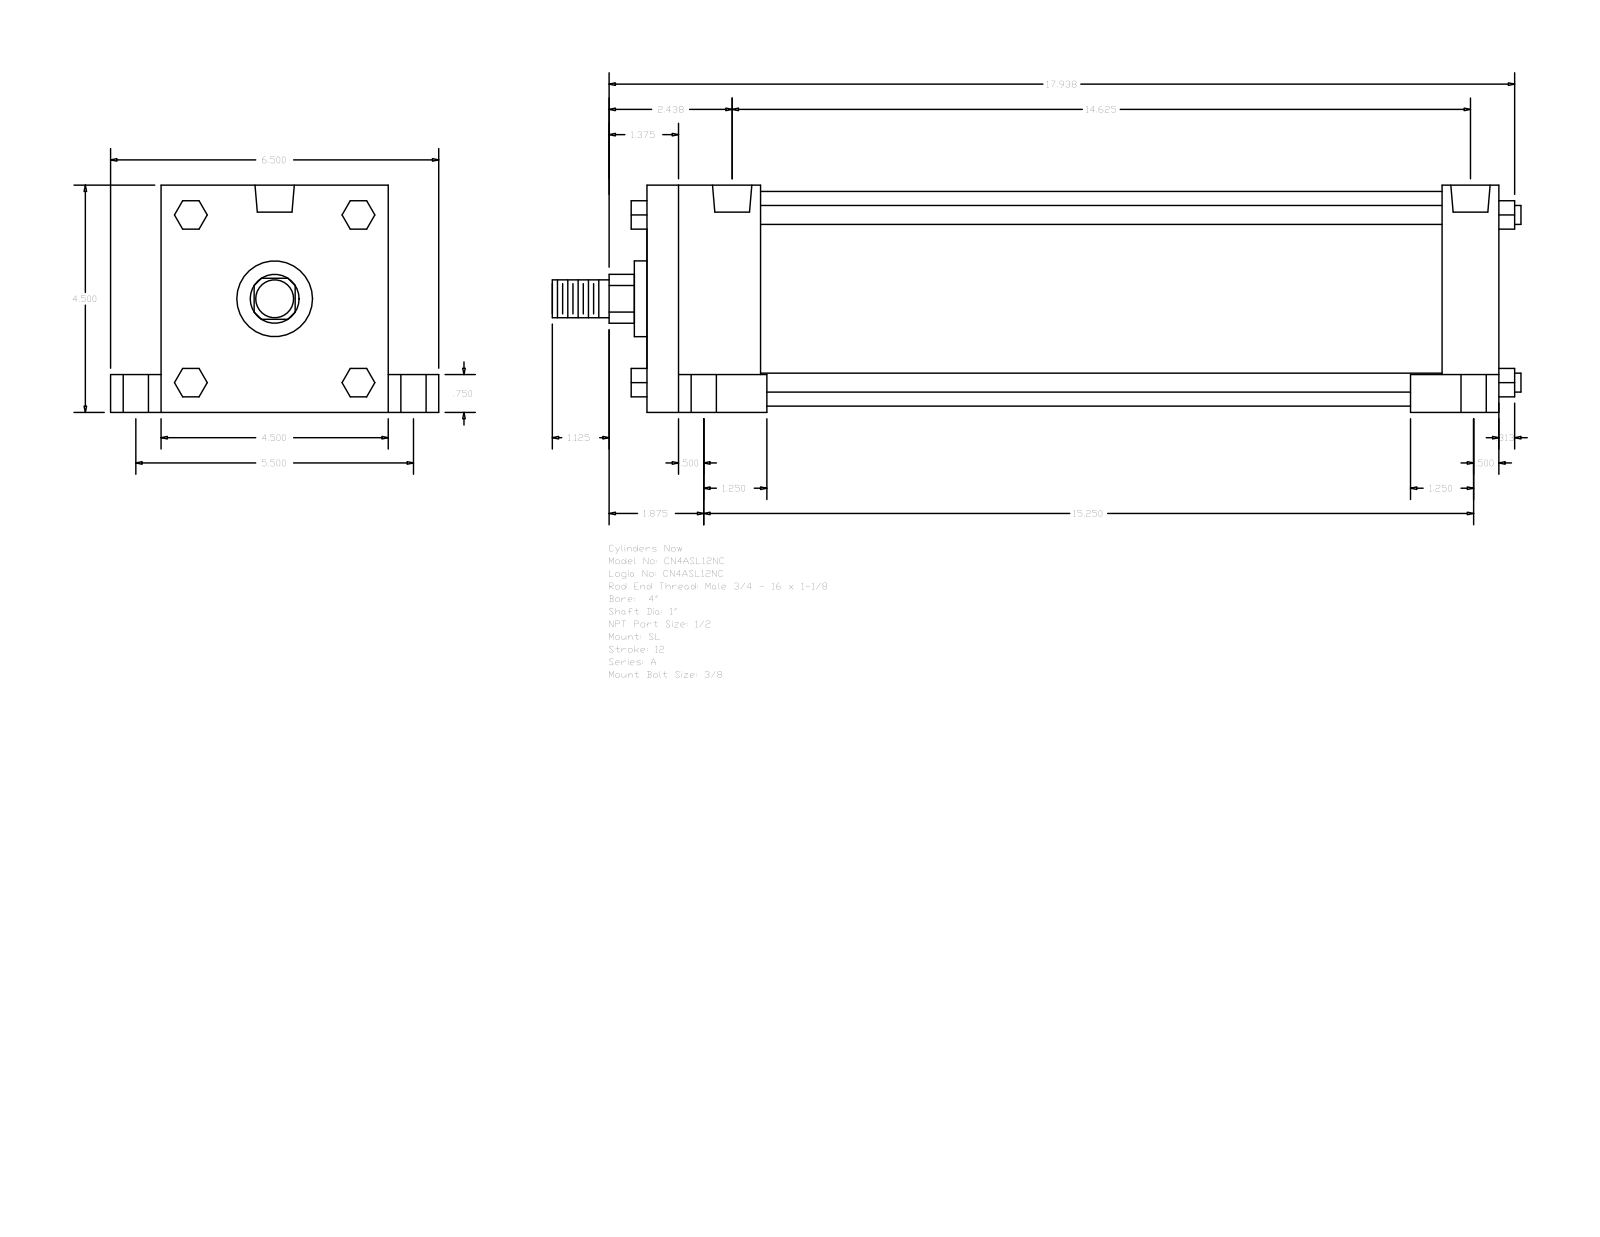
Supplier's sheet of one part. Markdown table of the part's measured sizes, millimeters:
| quantity | value |
| --- | --- |
| part name | A_SL__0400_1 |
| STEP written by | GSSL Pune (CONFIG_CONTROL_DESIGN) |
| units | millimeters |
| bodies | 0 solids, 150 faces (114 planar, 36 cylindrical, 0 other) |
| overall size | 487.36 × 165.1 × 114.3 |
| round holes (diameter × count) | 8.73 × 4, 12.7 × 4, 19.05 × 4, 19.77 × 2 |
| round bosses / shafts (diameter × count) | 9.53 × 4, 107.95 × 1, 38.1 × 1, 25.4 × 1, 19.05 × 1 |
| partial cylindrical surfaces (radius × count) | 12.29 × 1 |
| main face-to-face distances | 114.3, 428.63, 57.15, 371.48, 400.05, 342.9, 28.58, 19.05, 25.4, 139.7 |
| hole center spacings | 3.18, 69.87, 70.01, 71.3, 72, 139.7, 365.12, 368.3 |
